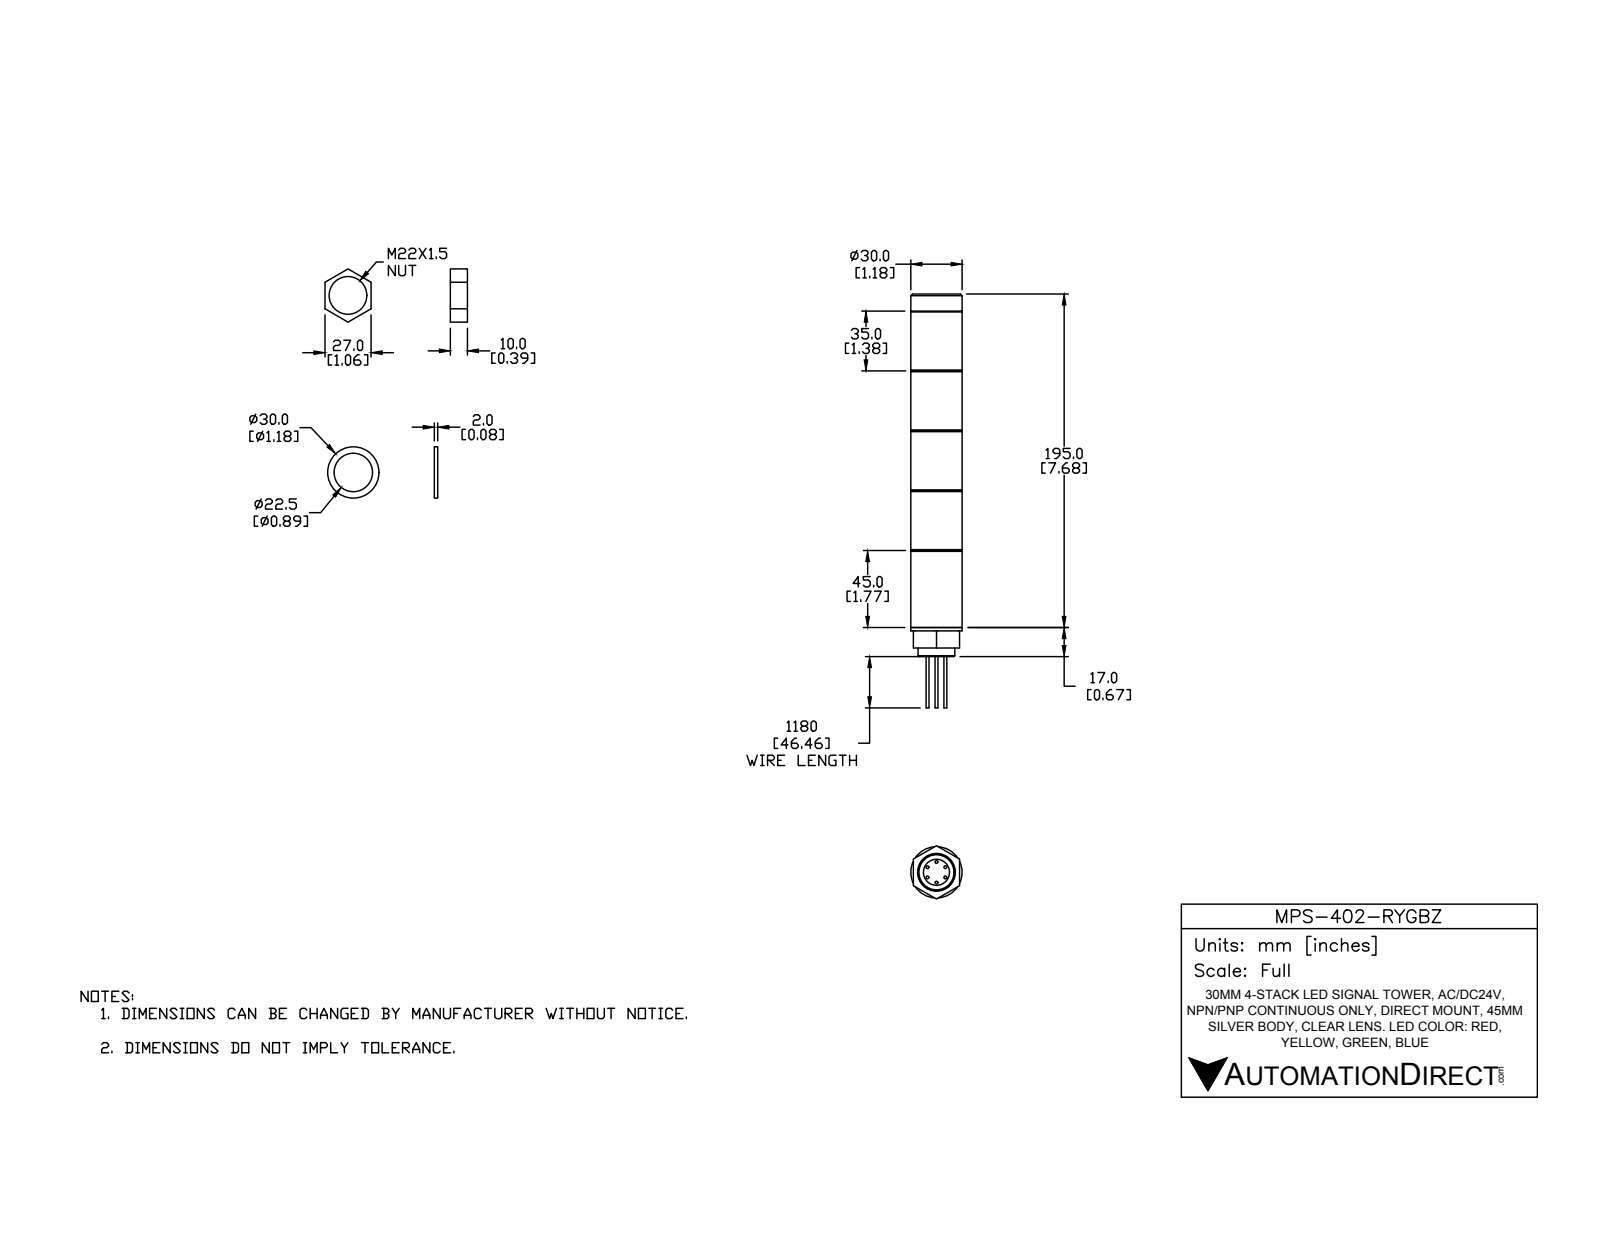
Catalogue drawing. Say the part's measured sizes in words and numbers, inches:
The part is named "MPS-402-RYGBZ". Its 3-D file was written by "SolidWorks 2016 (AUTOMOTIVE_DESIGN)". It is 15 solids with 119 faces: 53 planar, 42 cylindrical and 24 other. Overall it measures 9.528 by 1.228 by 1.181 inches. Its volume is 8.163 cubic inches and its surface area 57.21 square inches. Round holes: 1 of diameter 0.126, 1 of diameter 0.303, 1 of diameter 0.602, 1 of diameter 0.815, 1 of diameter 0.866. Round bosses or shafts: 6 of diameter 0.067, 1 of diameter 1.181, 1 of diameter 0.846, 1 of diameter 0.197. The main face-to-face distances are 1.378, 2.756, 4.134, 1.772, 3.15, 4.528, 5.906, 5.512, 1.85, 3.228.
